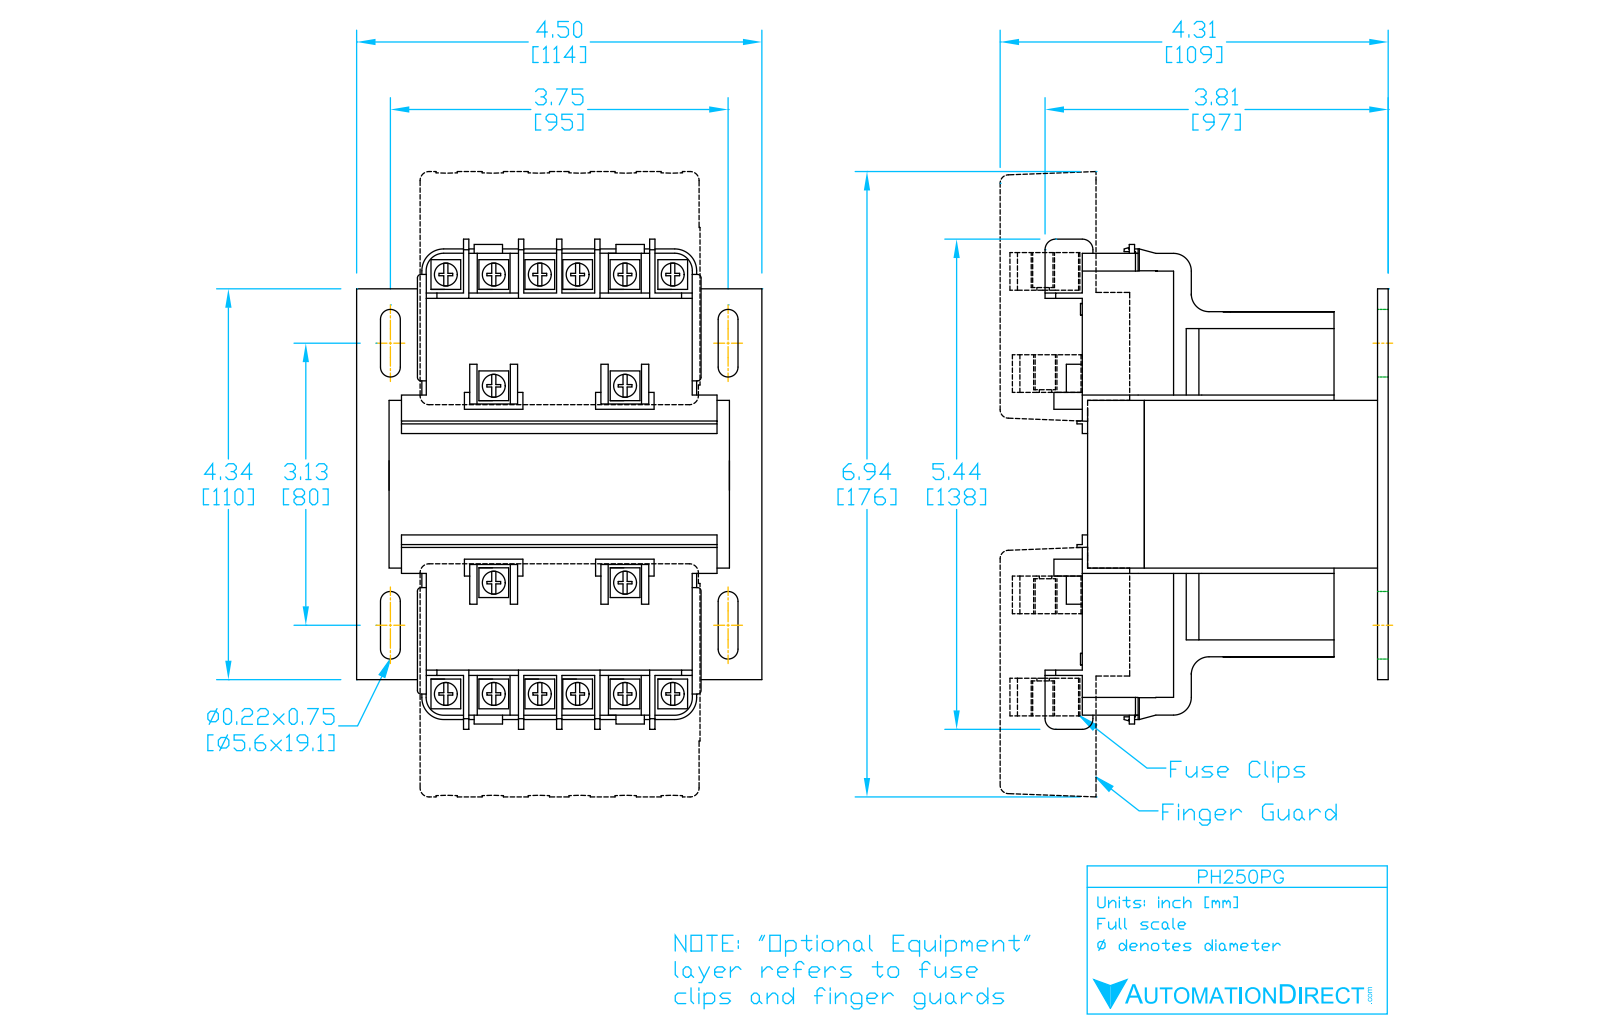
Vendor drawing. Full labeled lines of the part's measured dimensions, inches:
Part name (STEP PRODUCT): PH250PG
STEP written by: SolidWorks 2017 (AUTOMOTIVE_DESIGN)
Units: inches
Bodies: 8 solids, 592 faces (376 planar, 152 cylindrical, 64 other)
Overall size (bounding box): 5.35 × 4.5 × 3.74
Volume: 46.56 in³ · Surface area: 184.4 in²
Round holes (diameter × count): ⌀0.157 ×4
Partial cylindrical surfaces — rounded edges, fillets, slot ends (radius × count): R0.039 ×62, R0.197 ×16, R0.11 ×8, R0.1 ×4, R0.188 ×4, R0.243 ×4, R0.472 ×2
Main face-to-face distances: 1.772, 0.069, 2.52, 2.589, 1.033, 3.622, 1.102, 0.118, 0.63, 0.472
Hole centre spacings: 1.25, 3.375, 3.599
